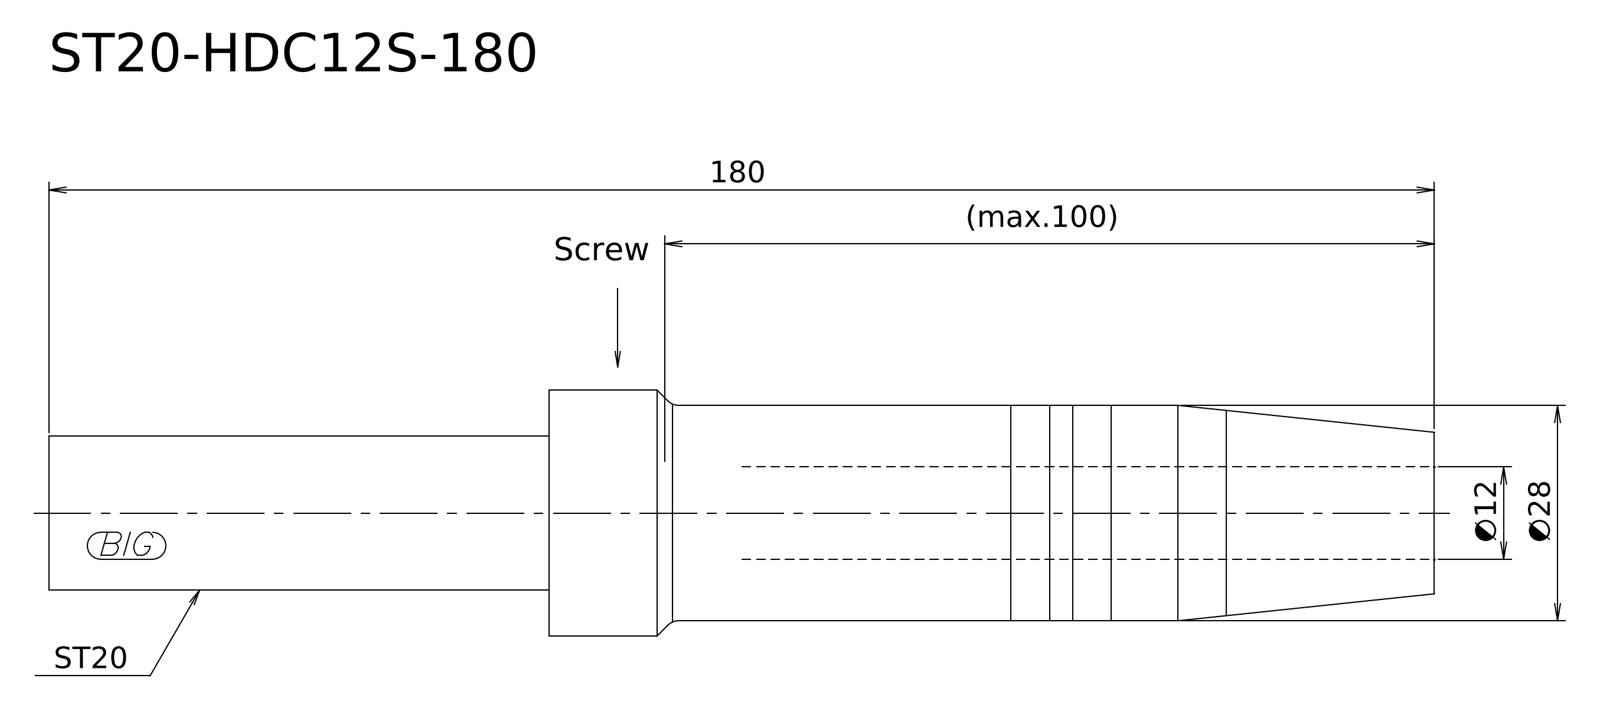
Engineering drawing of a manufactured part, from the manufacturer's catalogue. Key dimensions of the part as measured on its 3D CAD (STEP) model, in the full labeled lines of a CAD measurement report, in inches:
STEP written by: Kubotek KeyCreator V8.5.1 (14335) (CONFIG_CONTROL_DESIGN)
Units: inches
Bodies: 1 solid, 9 faces (3 planar, 3 cylindrical, 3 other)
Overall size (bounding box): 7.087 × 1.26 × 1.26
Volume: 5.454 in³ · Surface area: 23.65 in²
Round bosses / shafts (diameter × count): ⌀1.26 ×1, ⌀1.102 ×1, ⌀0.787 ×1
Main face-to-face distances: 4.528, 7.087, 2.559
